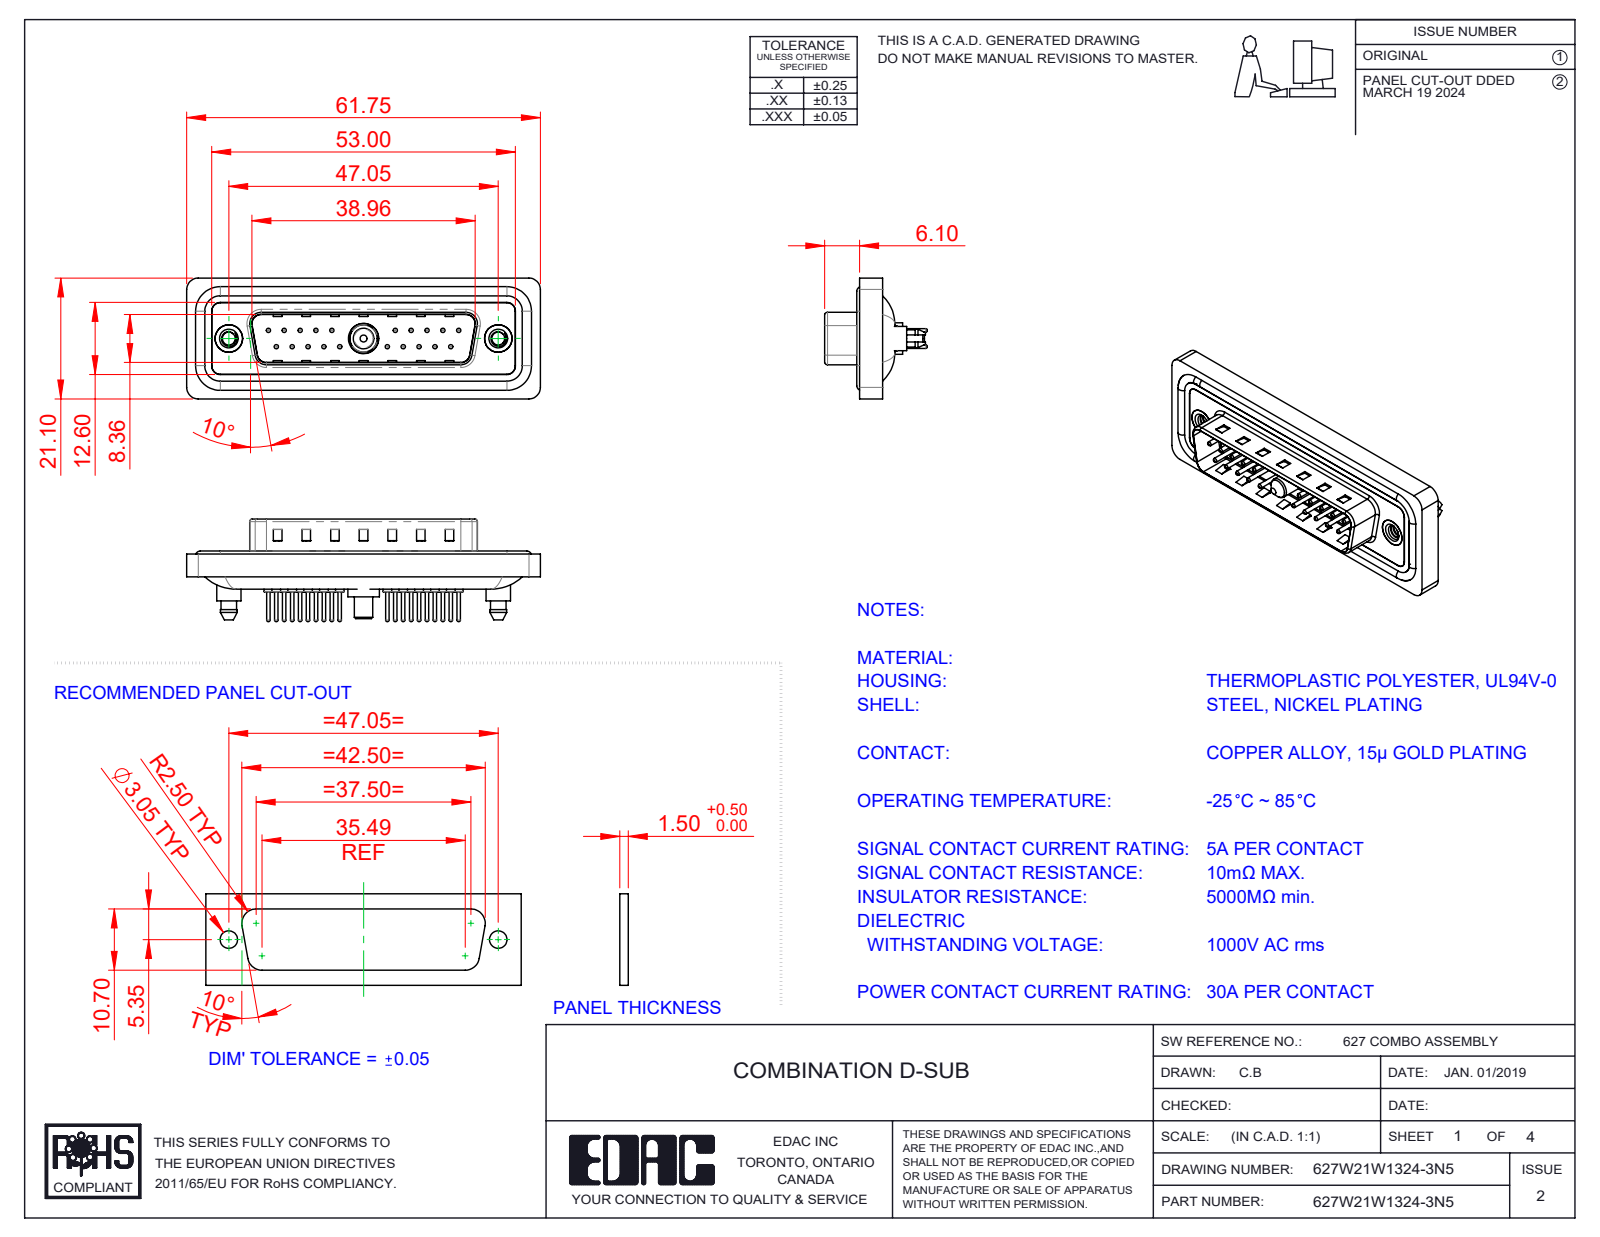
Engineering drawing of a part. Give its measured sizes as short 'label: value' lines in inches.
name: 627Combo Waterproof Housing_25 Contacts; 627Combo Shell Front_25 Contacts; 627Combo Contact Row 2_24; 627Combo Threaded Boardlock_5 (+5 more)
written by: SolidWorks 2023 (CONFIG_CONTROL_DESIGN)
unit: in
bodies: 29 solids, 1312 faces (375 planar, 519 cylindrical, 418 other)
size: 2.431 × 0.831 × 0.705
volume: 0.448 in³; area: 19.05 in²
holes: 20× ⌀0.03, 20× ⌀0.063, 20× ⌀0.079, 2× ⌀0.089, 2× ⌀0.157, 2× ⌀0.189, 2× ⌀0.197, 1× ⌀0.191, 1× ⌀0.209
bosses: 20× ⌀0.059, 20× ⌀0.024, 4× ⌀0.063, 2× ⌀0.213, 2× ⌀0.193, 2× ⌀0.167, 1× ⌀0.217, 1× ⌀0.205
rounds: 24× R0.059, 18× R0.079, 10× R0.063, 8× R0.02, 4× R0.01, 4× R0.024, 4× R0.026, 4× R0.035
face distances: 0.016, 0.059, 0.043, 0.063, 0.02, 0.122, 0.114, 0.161, 0.032, 0.377
hole spacings: 0.124, 0.109, 0.218, 0.327, 0.198, 0.763, 0.826, 0.872
